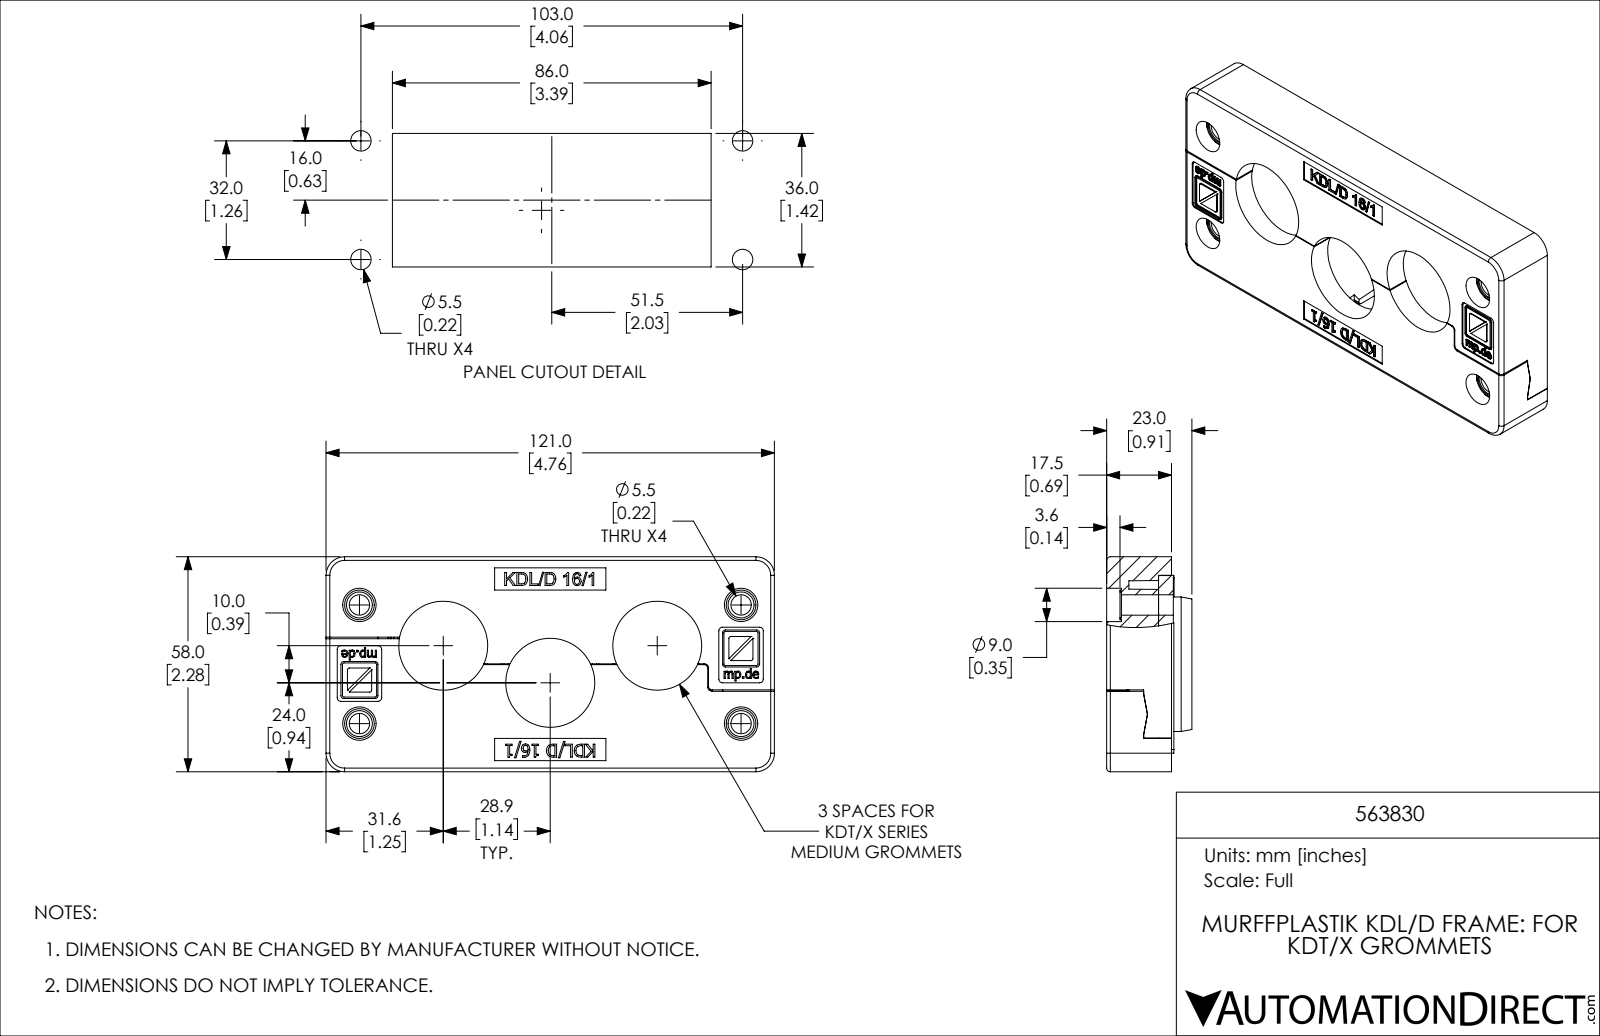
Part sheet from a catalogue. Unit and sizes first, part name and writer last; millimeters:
Units: millimetres
Overall size (bounding box): 121 × 58 × 23
Round holes (diameter × count): ⌀5 ×4, ⌀5.5 ×4, ⌀7 ×4, ⌀9 ×4, ⌀24.95 ×3, ⌀6 ×2, ⌀24 ×1
Round bosses / shafts (diameter × count): ⌀8 ×4
Partial cylindrical surfaces — rounded edges, fillets, slot ends (radius × count): R1 ×42, R0.5 ×19, R0.4 ×12, R0.8 ×8, R0.1 ×4, R0.15 ×4, R0.3 ×4, R5 ×4
Main face-to-face distances: 5, 6, 14, 3.5, 4, 53, 18, 12, 58, 0.5
Hole centre spacings: 10, 22, 7.5, 25.15, 52.66, 81.13, 12, 14.5
Volume: 95 130 mm³ · Surface area: 45 062 mm²
Bodies: 3 solids, 1133 faces (603 planar, 209 cylindrical, 321 other)
Part name (STEP PRODUCT): 563830
STEP written by: SolidWorks 2019 (CONFIG_CONTROL_DESIGN)
